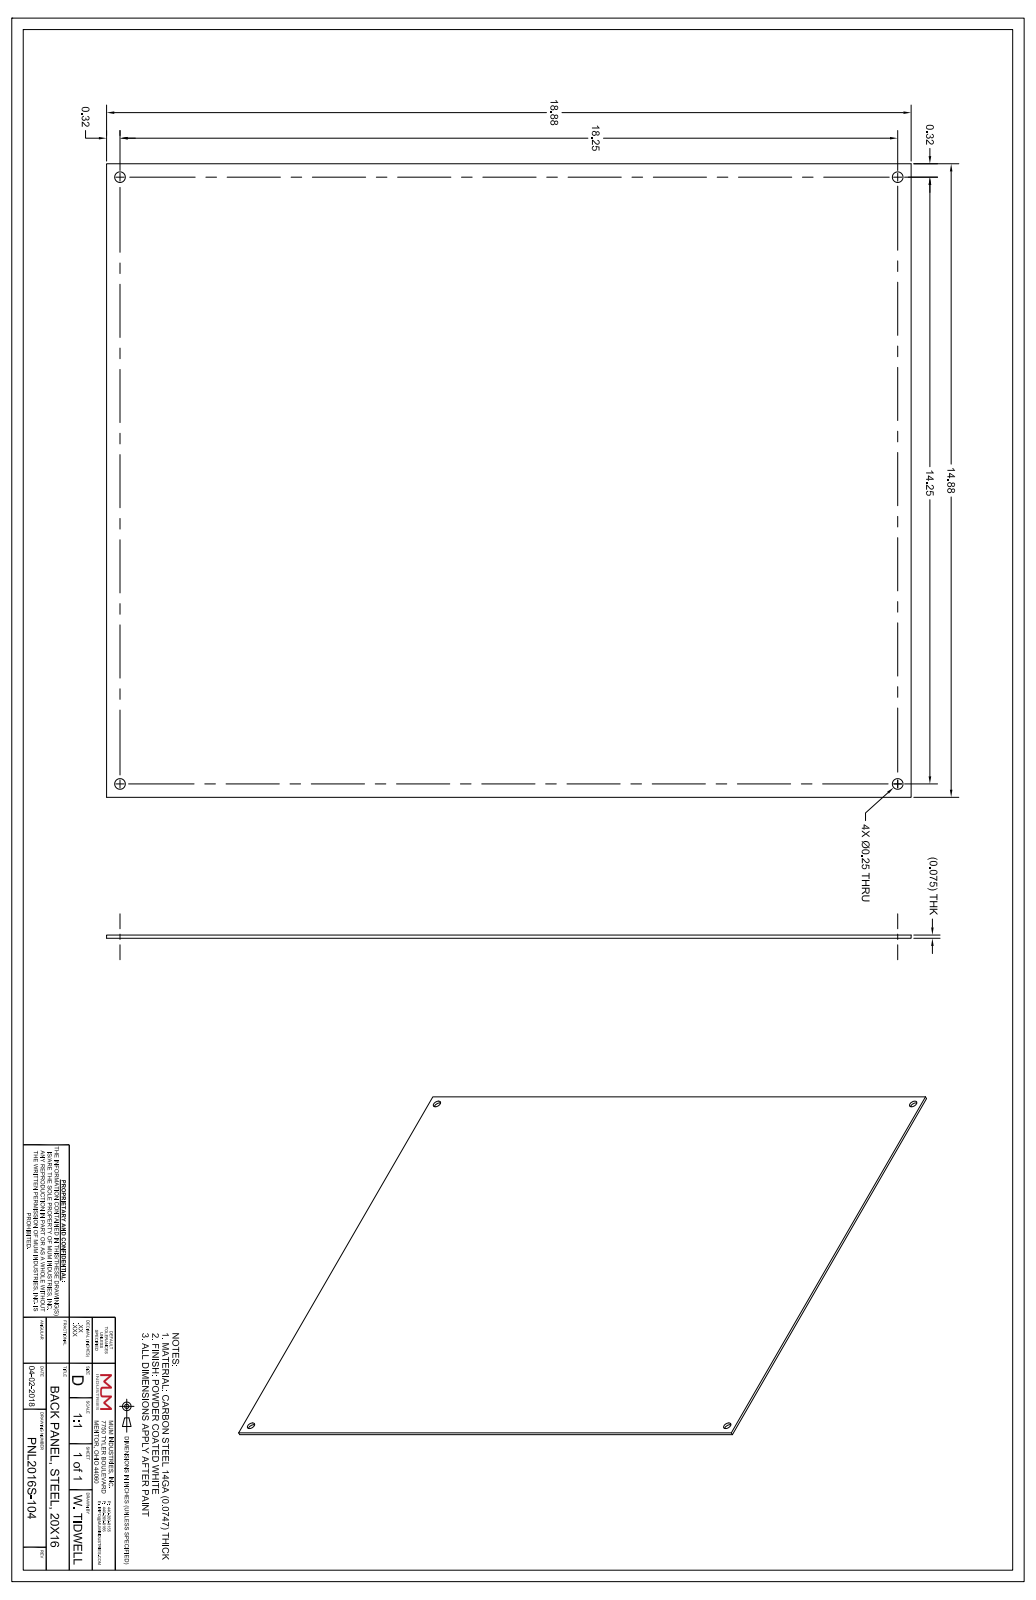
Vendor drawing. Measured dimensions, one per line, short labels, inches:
name: SBP-2016-P10
written by: SolidWorks 2018 (AUTOMOTIVE_DESIGN)
unit: in
bodies: 1 solid, 10 faces (6 planar, 4 cylindrical, 0 other)
size: 18.88 × 14.88 × 0.075
volume: 20.97 in³; area: 566.8 in²
holes: 4× ⌀0.25
face distances: 0.075, 14.88, 18.88
hole spacings: 14.25, 18.25, 23.154
